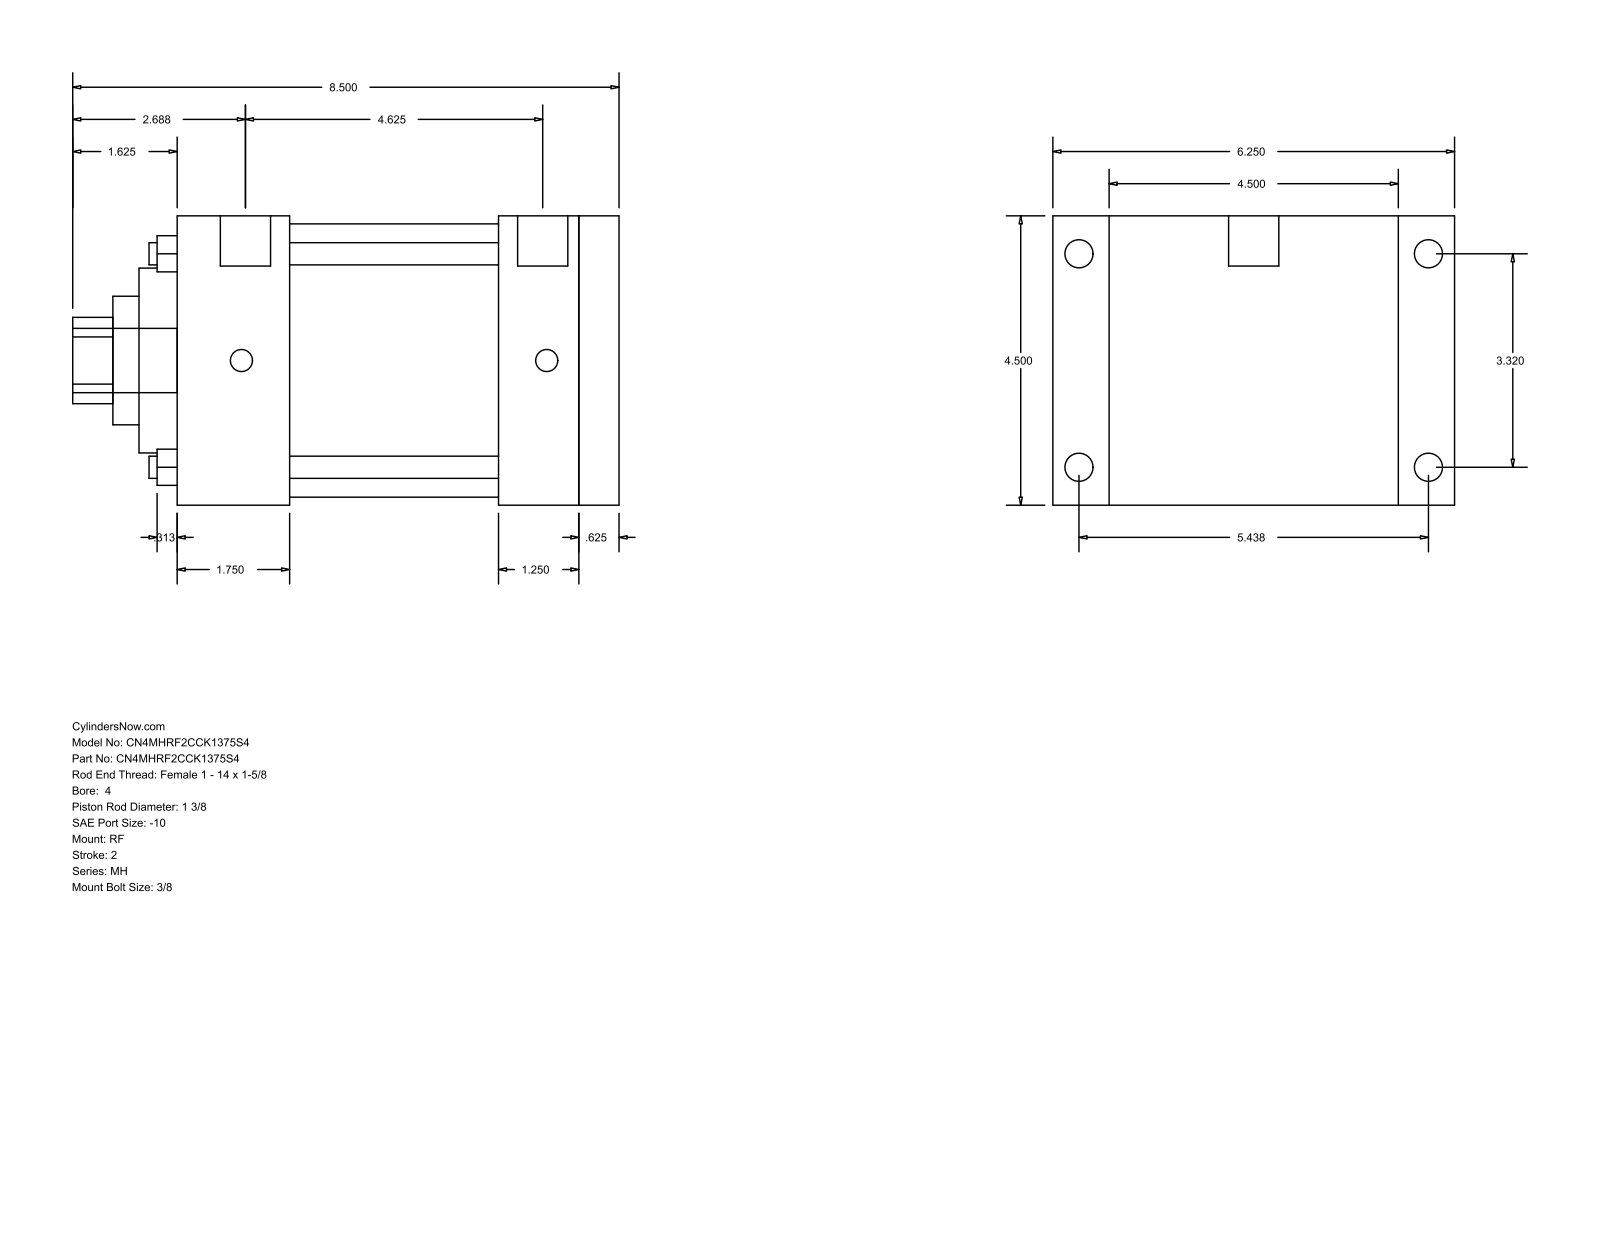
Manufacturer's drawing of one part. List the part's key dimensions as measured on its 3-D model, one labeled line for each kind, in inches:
Part name (STEP PRODUCT): MH_RF__0400_1.375
STEP written by: GSSL Pune (CONFIG_CONTROL_DESIGN)
Units: inches
Bodies: 0 solids, 94 faces (65 planar, 29 cylindrical, 0 other)
Overall size (bounding box): 8.5 × 6.25 × 4.5
Round holes (diameter × count): ⌀0.345 ×4, ⌀1.375 ×1, ⌀2 ×1, ⌀2.875 ×1, ⌀4.25 ×1
Round bosses / shafts (diameter × count): ⌀0.438 ×4, ⌀0.344 ×4, ⌀0.781 ×2, ⌀1 ×1
Partial cylindrical surfaces — rounded edges, fillets, slot ends (radius × count): R0.672 ×1
Main face-to-face distances: 4.5, 6.875, 6.25, 0.625, 1.75, 4.5, 5.125, 5, 3.25, 1.25
Hole centre spacings: 2.347, 3.32, 4.695
